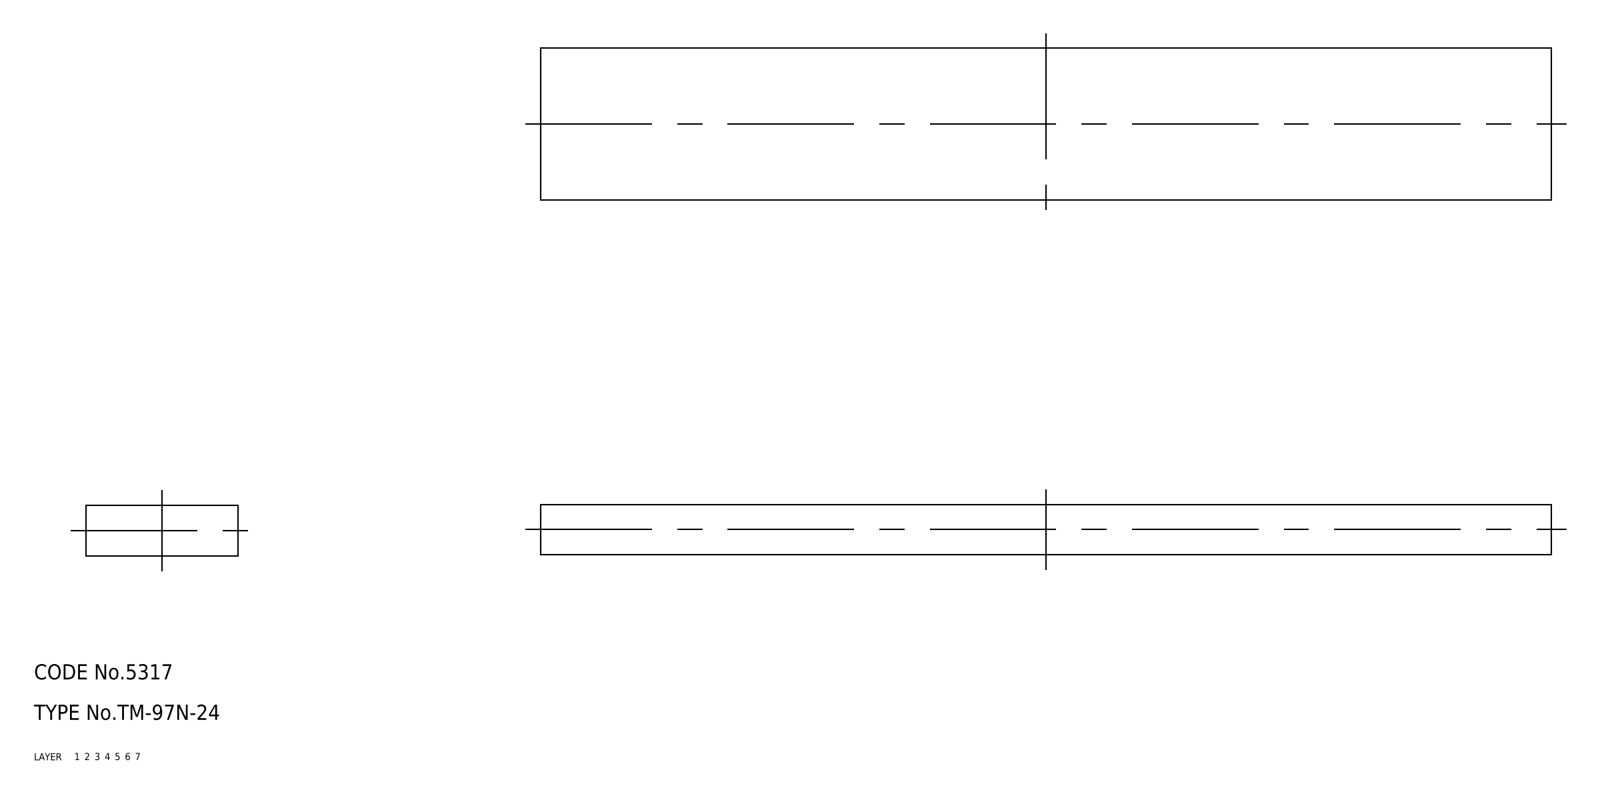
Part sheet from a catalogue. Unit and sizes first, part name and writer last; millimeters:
Units: millimetres
Overall size (bounding box): 200 × 30 × 10
Volume: 60 000 mm³ · Surface area: 16 600 mm²
Bodies: 1 solid, 6 faces (0 planar, 0 cylindrical, 6 other)
Part name (STEP PRODUCT): rubber foam
STEP written by: CADfix (AUTOMOTIVE_DESIGN)
